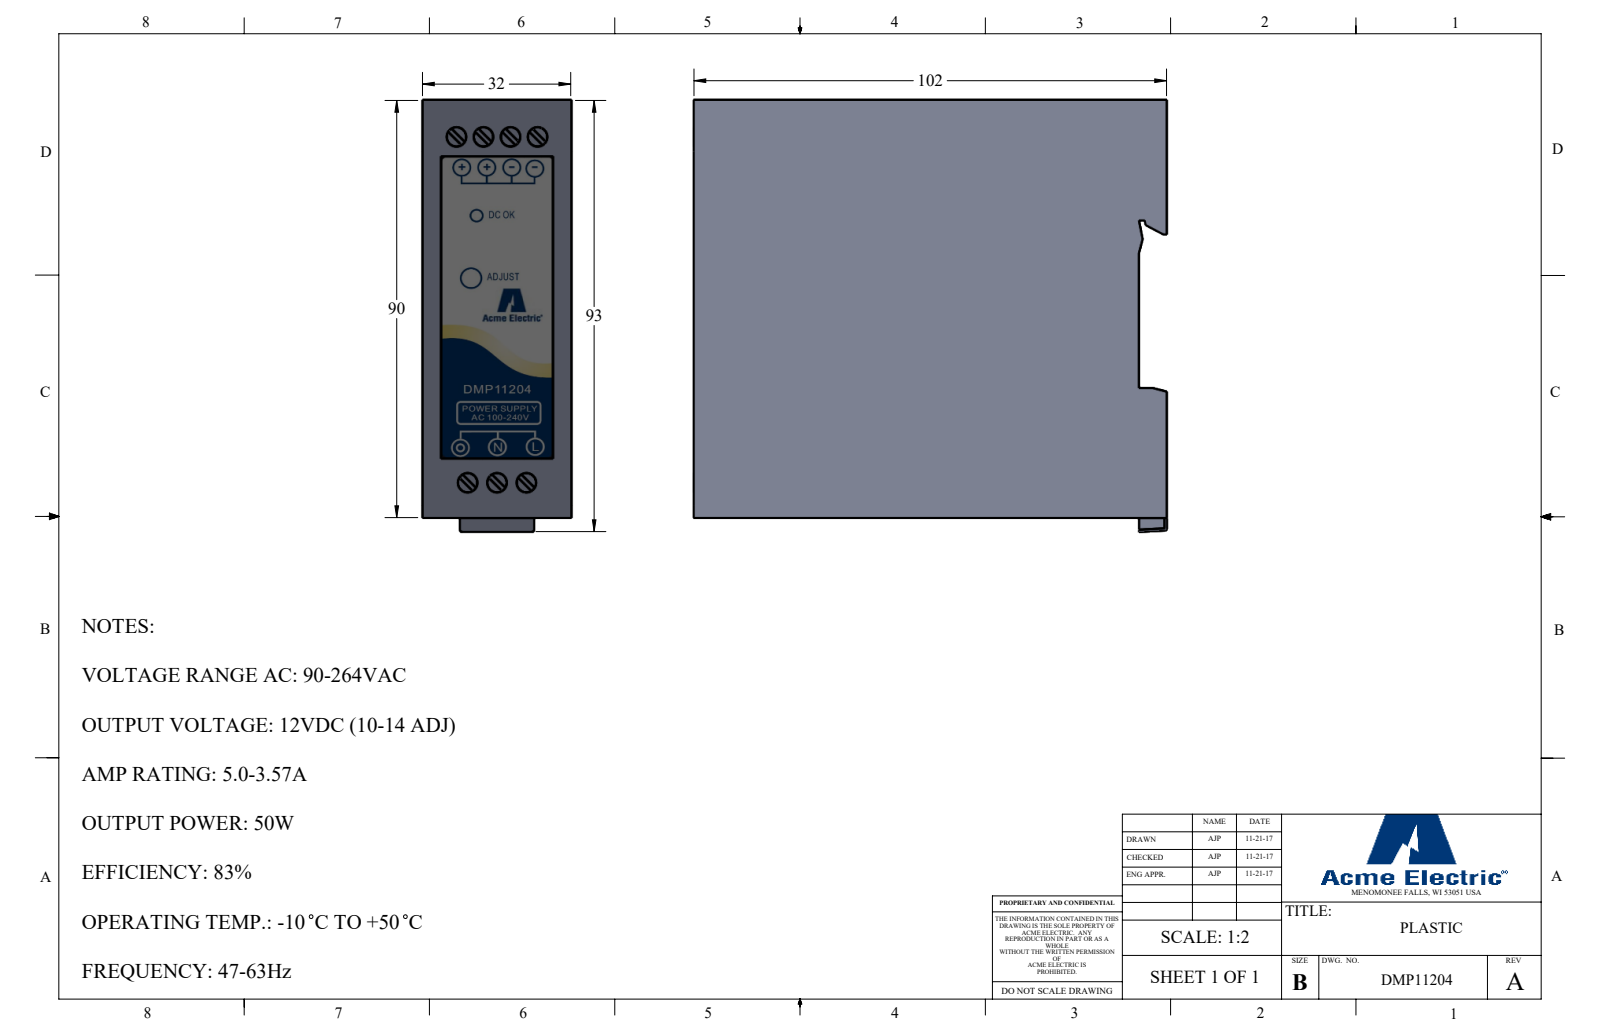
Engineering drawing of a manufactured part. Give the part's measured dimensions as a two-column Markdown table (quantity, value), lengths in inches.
| quantity | value |
| --- | --- |
| part name | DMP11204 |
| STEP written by | SolidWorks 2017 (AUTOMOTIVE_DESIGN) |
| units | inches |
| bodies | 1 solid, 77 faces (56 planar, 19 cylindrical, 2 other) |
| overall size | 4.016 × 3.661 × 1.26 |
| volume | 17.54 in³ |
| surface area | 48.01 in² |
| round holes (diameter × count) | 0.165 × 7 |
| partial cylindrical surfaces (radius × count) | 0.02 × 5 |
| main face-to-face distances | 1.26, 3.543, 4.016, 0.236, 3.78, 1.102, 2.441, 0.039, 3.976, 3.74 |
| hole center spacings | 0.228, 0.248, 0.457, 2.931, 2.931, 2.932, 2.949, 2.952 |
